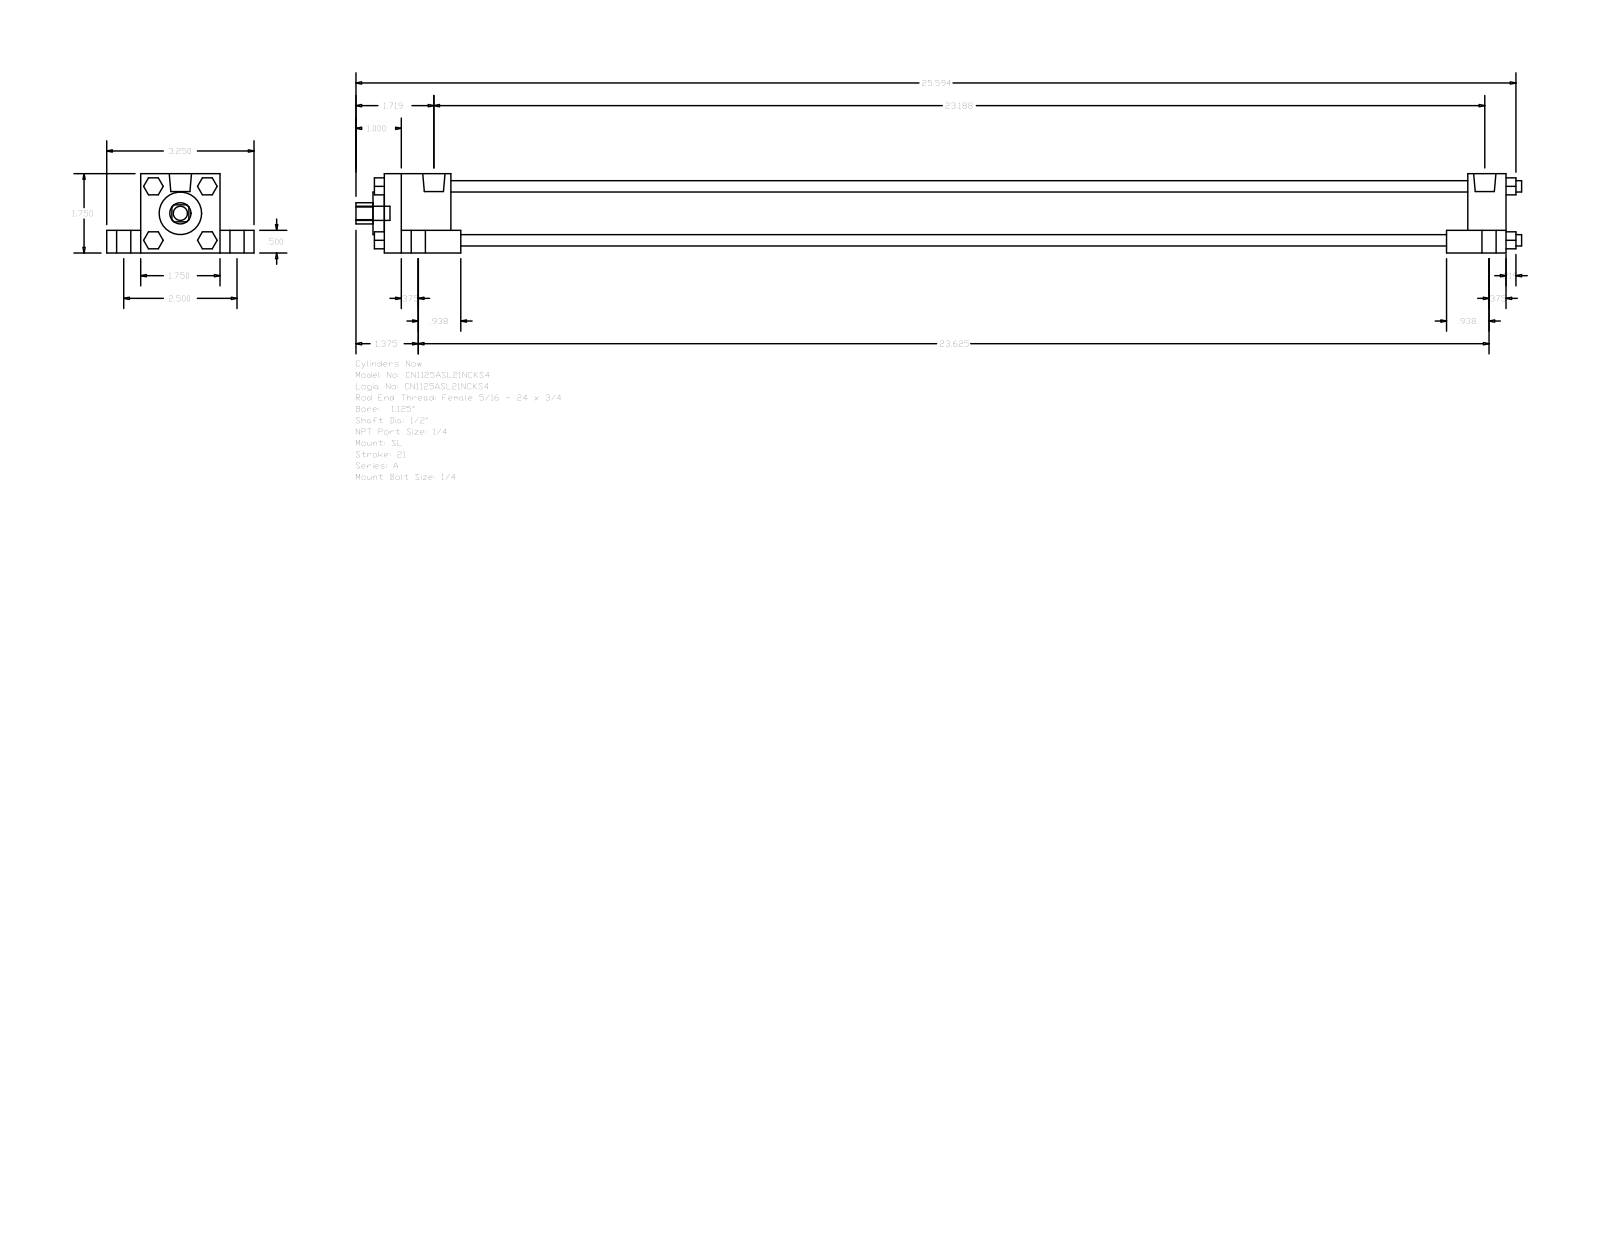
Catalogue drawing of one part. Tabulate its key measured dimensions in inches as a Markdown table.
| quantity | value |
| --- | --- |
| part name | A_SL__0112_0.5 |
| STEP written by | GSSL Pune (CONFIG_CONTROL_DESIGN) |
| units | inches |
| bodies | 0 solids, 150 faces (114 planar, 36 cylindrical, 0 other) |
| overall size | 25.719 × 3.25 × 1.75 |
| round holes (diameter × count) | 0.5 × 1, 0.937 × 1, 1.255 × 1 |
| round bosses / shafts (diameter × count) | 0.313 × 5, 0.563 × 4, 0.25 × 4, 0.219 × 4, 0.492 × 2 |
| partial cylindrical surfaces (radius × count) | 0.234 × 1 |
| main face-to-face distances | 1.75, 1.25, 0.5, 0.75, 2.5, 23.281, 24.75, 23.906, 0.844, 1.469 |
